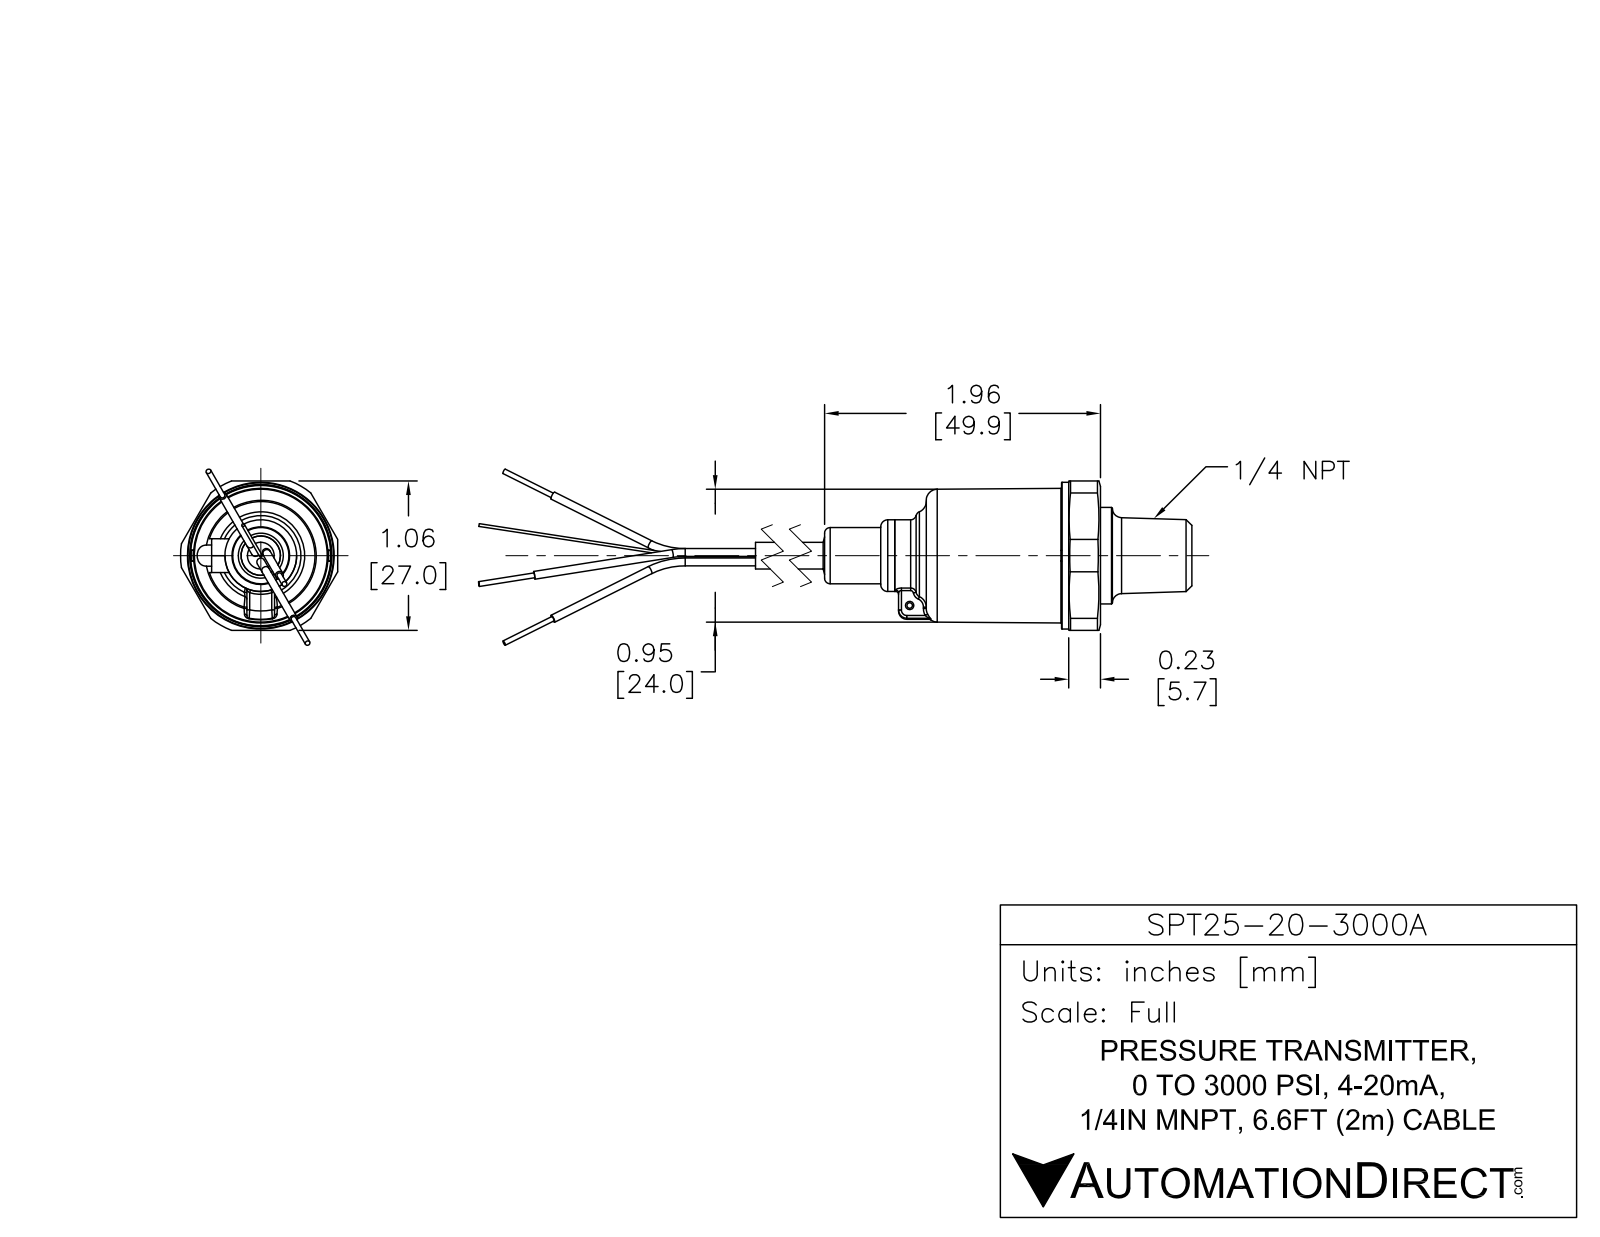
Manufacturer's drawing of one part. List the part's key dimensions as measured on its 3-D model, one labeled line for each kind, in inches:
Part name (STEP PRODUCT): SPT25-20-3000A
STEP written by: SolidWorks 2017 (AUTOMOTIVE_DESIGN)
Units: inches
Bodies: 7 solids, 116 faces (32 planar, 49 cylindrical, 35 other)
Overall size (bounding box): 6.035 × 1.142 × 1.067
Volume: 1.269 in³ · Surface area: 11.11 in²
Round holes (diameter × count): ⌀0.039 ×1, ⌀0.13 ×1
Round bosses / shafts (diameter × count): ⌀0.055 ×6, ⌀0.03 ×5, ⌀1.053 ×1, ⌀0.945 ×1, ⌀0.689 ×1, ⌀0.551 ×1, ⌀0.512 ×1, ⌀0.394 ×1
Partial cylindrical surfaces — rounded edges, fillets, slot ends (radius × count): R0.079 ×1, R0.571 ×1
Main face-to-face distances: 0.266, 0.945, 0.679, 1.683, 1.949, 2.628, 1.732, 0.049, 0.217, 0.896
